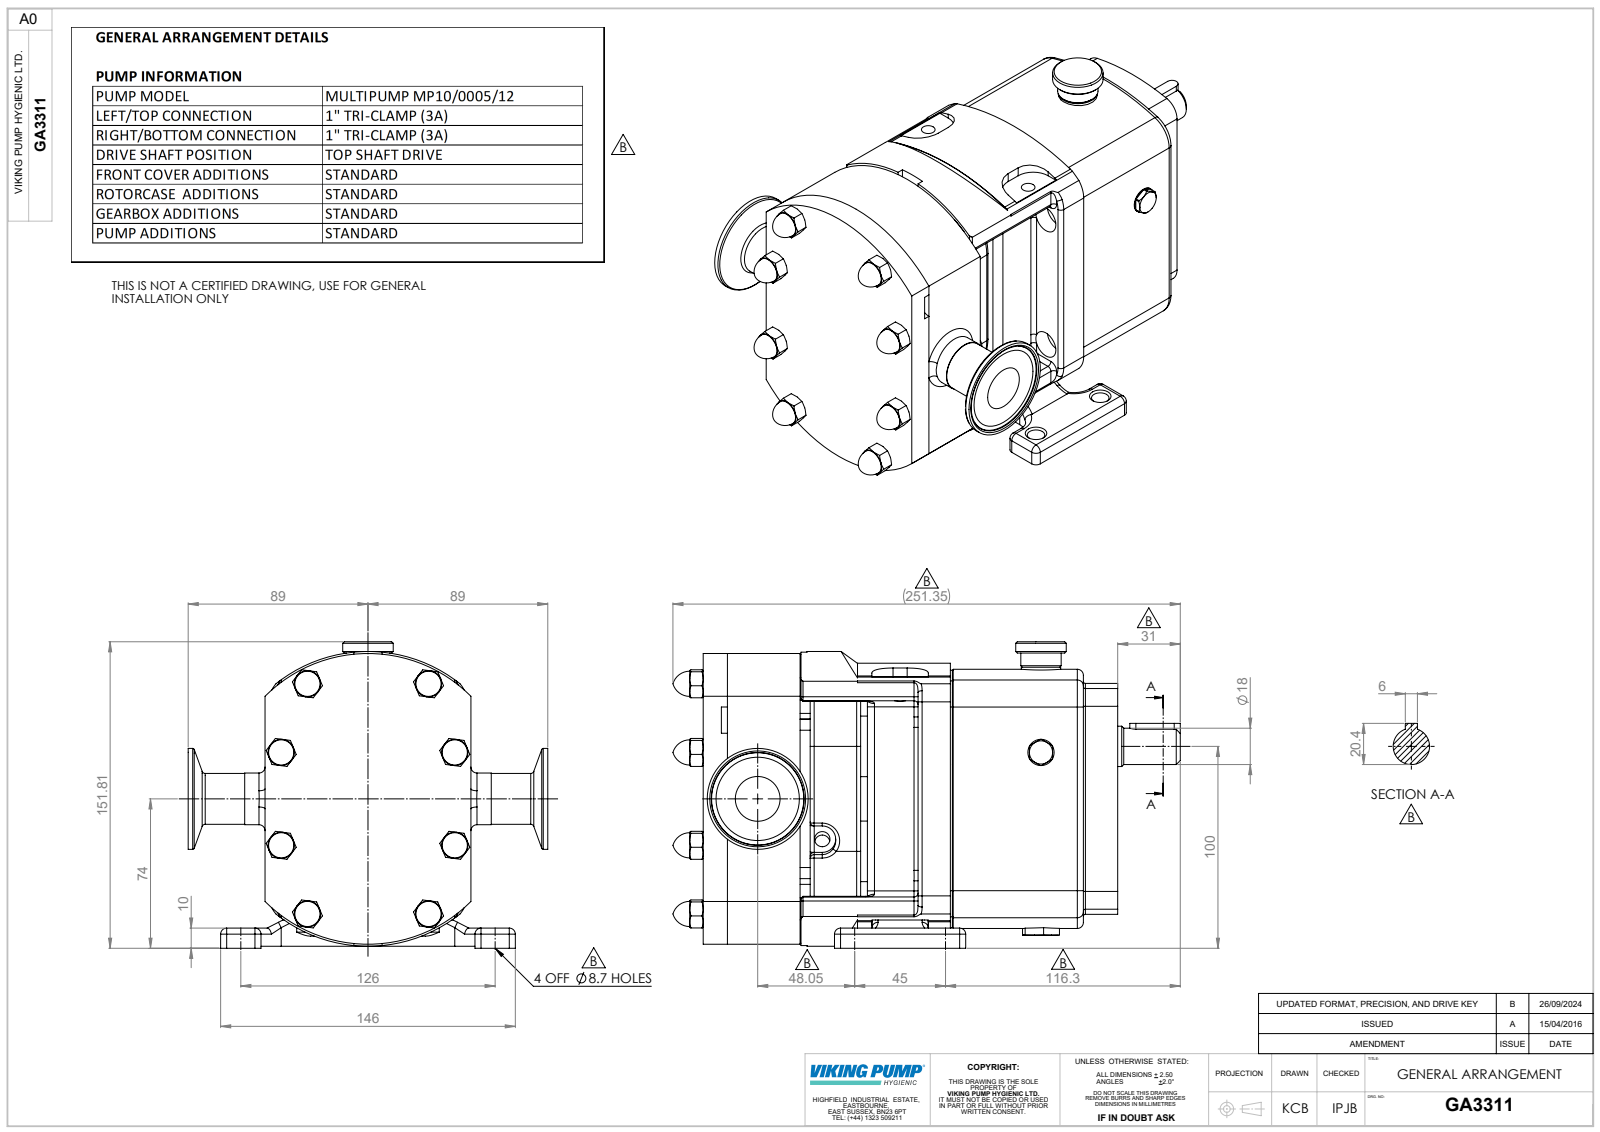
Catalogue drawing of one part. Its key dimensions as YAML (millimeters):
part_name: "Copy of Z94-5121-11 - 1 INCH v2^GA3311; Copy (2) of CP10-0005-12 H T^GA3311; GA3311"
step_written_by: "SolidWorks 2023 (AUTOMOTIVE_DESIGN)"
units: millimeters
bodies: {solids: 3, faces: 763, planar: 252, cylindrical: 218, other: 293}
overall_size: [251.35, 178.15, 151.81]
volume: 2253000
surface_area: 181750
round_holes:
  - {diameter: 8.7, count: 4}
  - {diameter: 14, count: 4}
  - {diameter: 6.8, count: 2}
  - {diameter: 7.63, count: 2}
  - {diameter: 22.2, count: 1}
  - {diameter: 22.3, count: 1}
  - {diameter: 22.53, count: 1}
round_bosses_or_shafts:
  - {diameter: 30, count: 2}
  - {diameter: 50, count: 1}
  - {diameter: 25.6, count: 1}
  - {diameter: 25.2, count: 1}
  - {diameter: 25.02, count: 1}
  - {diameter: 19.99, count: 1}
  - {diameter: 19.98, count: 1}
  - {diameter: 19.5, count: 1}
partial_cylinders:
  - {radius: 2, count: 30}
  - {radius: 3, count: 26}
  - {radius: 13.5, count: 12}
  - {radius: 10.5, count: 8}
  - {radius: 3.5, count: 6}
  - {radius: 5.5, count: 4}
  - {radius: 6, count: 4}
  - {radius: 9, count: 4}
face_to_face_distances: [5, 205.35, 124, 91.99, 81.35, 96.99, 102, 97, 5.01, 48]
hole_center_spacings: [35.92, 100.55, 45, 76, 77.02, 108.2, 126, 133.79]
